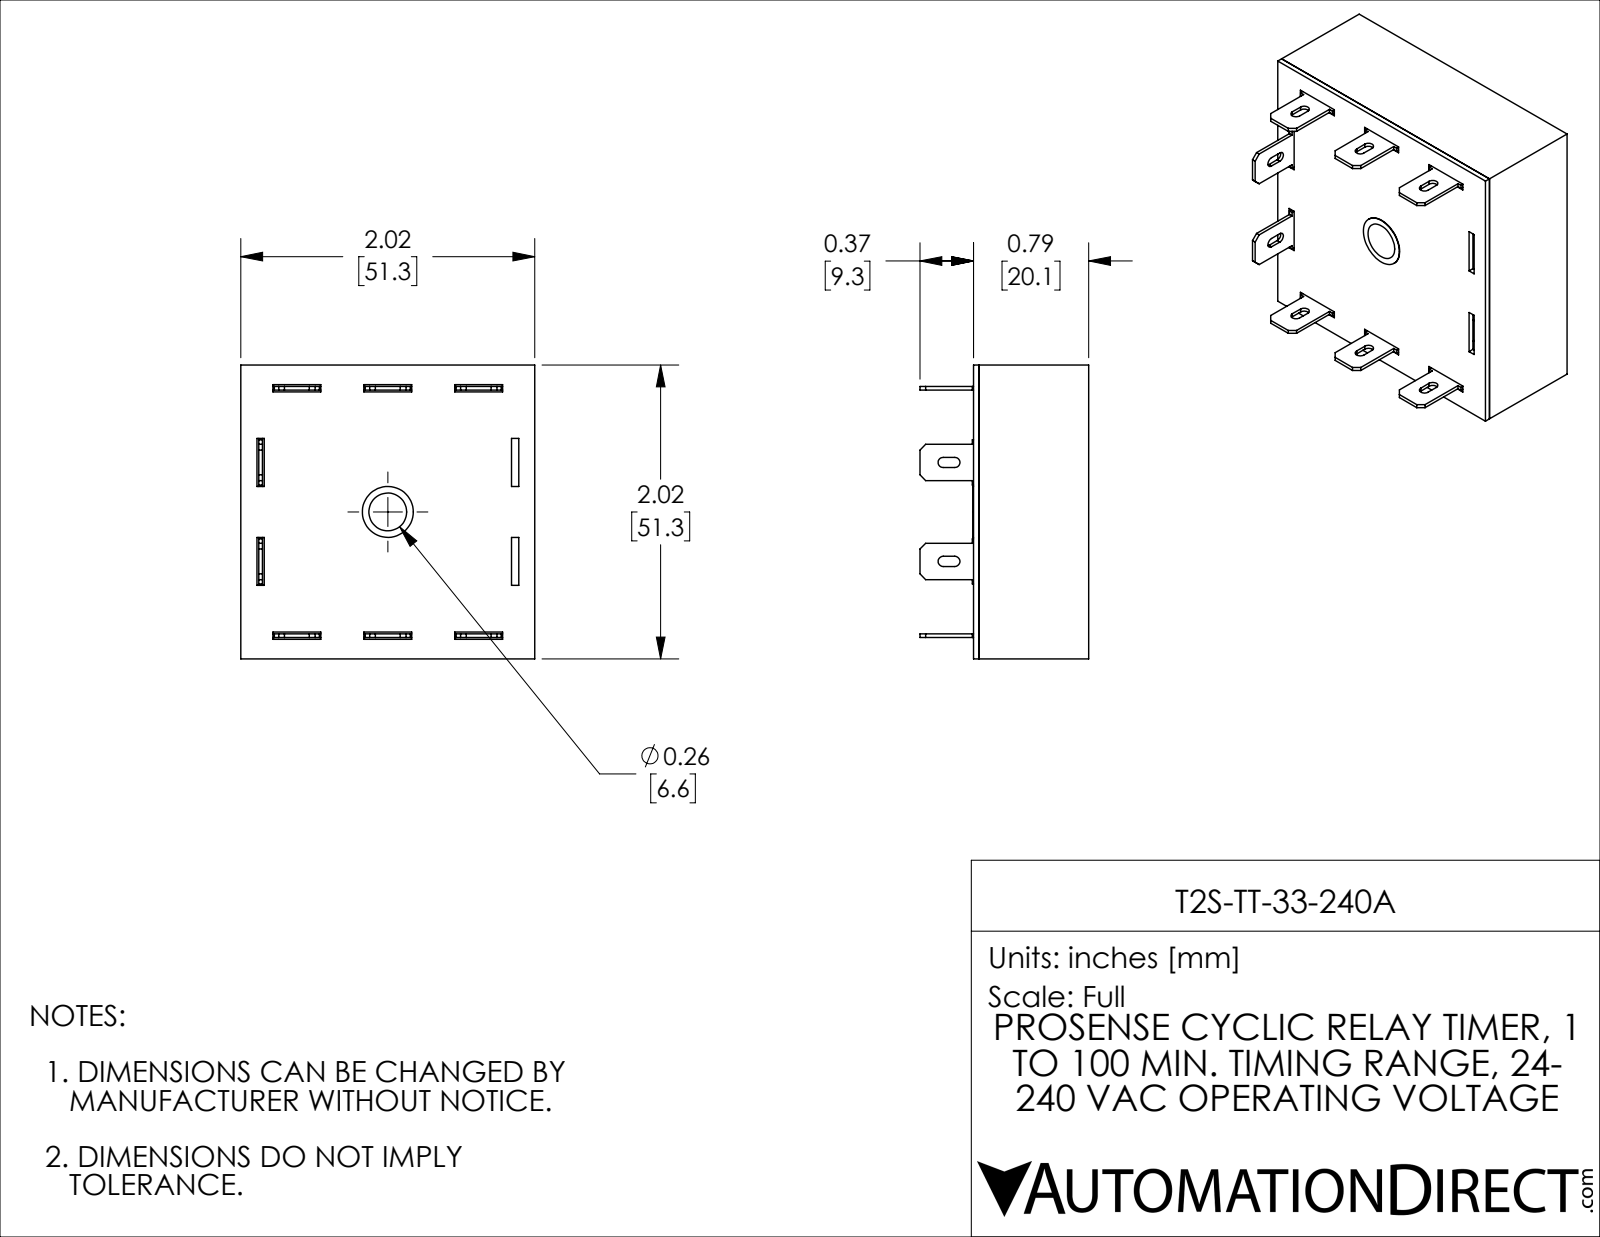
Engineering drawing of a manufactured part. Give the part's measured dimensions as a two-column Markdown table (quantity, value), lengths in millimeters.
| quantity | value |
| --- | --- |
| part name | T2S-TT-33-240A |
| STEP written by | SolidWorks 2021 (CONFIG_CONTROL_DESIGN) |
| units | millimeters |
| bodies | 10 solids, 256 faces (234 planar, 20 cylindrical, 2 other) |
| overall size | 51.31 × 51.31 × 29.46 |
| volume | 11 042 mm³ |
| surface area | 22 819 mm² |
| round holes (diameter × count) | 8.89 × 1 |
| partial cylindrical surfaces (radius × count) | 0.89 × 10 |
| main face-to-face distances | 1.14, 50.16, 19.15, 20.12, 0.97, 18.01, 18.98, 51.3, 49.02, 3.74 |
